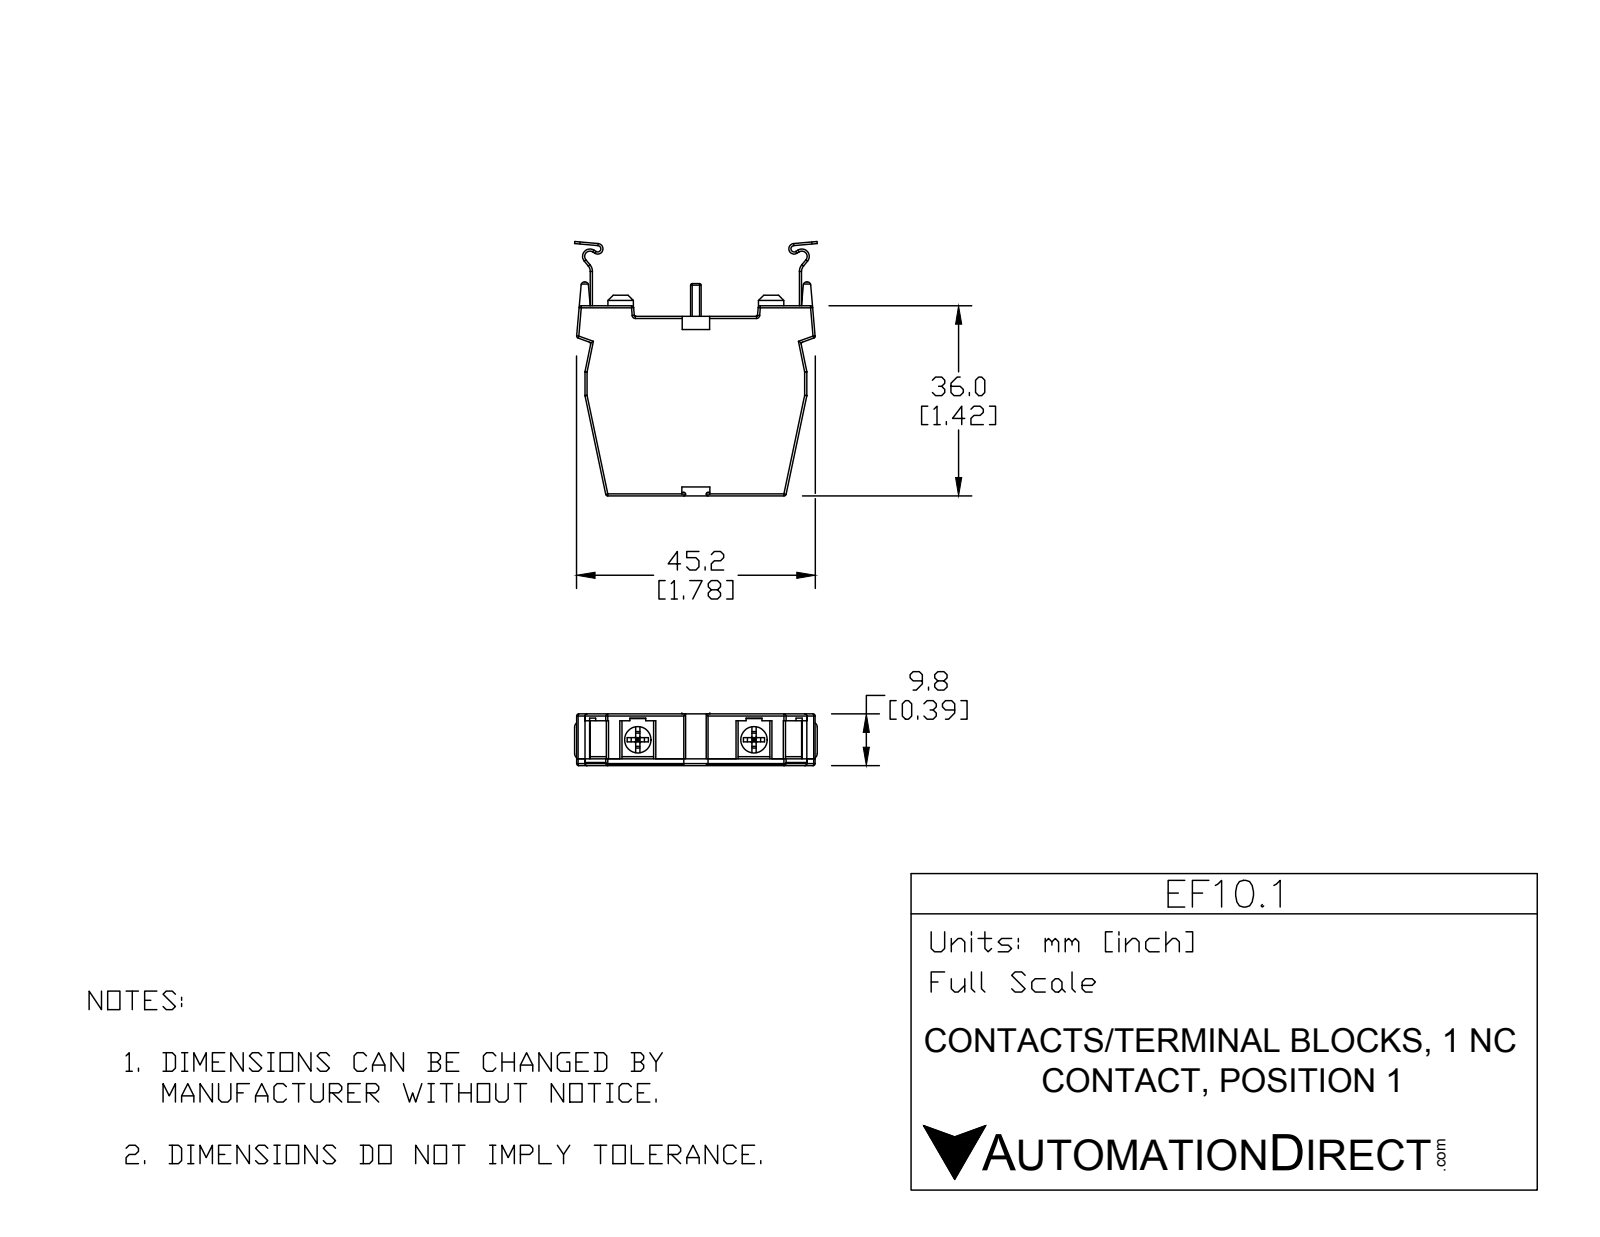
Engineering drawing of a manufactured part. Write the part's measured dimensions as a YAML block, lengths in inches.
part_name: "EF10.1"
step_written_by: "SolidWorks 2015 (AUTOMOTIVE_DESIGN)"
units: inches
bodies: {solids: 7, faces: 277, planar: 155, cylindrical: 100, other: 22}
overall_size: [1.896, 1.822, 0.386]
volume: 0.742
surface_area: 10.33
round_holes:
  - {diameter: 0.197, count: 4}
round_bosses_or_shafts:
  - {diameter: 0.187, count: 2}
  - {diameter: 0.157, count: 2}
partial_cylinders:
  - {radius: 0.01, count: 44}
  - {radius: 0.02, count: 8}
  - {radius: 0.039, count: 6}
  - {radius: 0.024, count: 4}
  - {radius: 0.024, count: 2}
  - {radius: 0.039, count: 2}
  - {radius: 0.055, count: 2}
  - {radius: 0.063, count: 2}
face_to_face_distances: [0.386, 0.055, 0.331, 1.339, 0.276, 0.016, 0.079, 0.125, 1.464, 0.138]
hole_center_spacings: [0.859]
